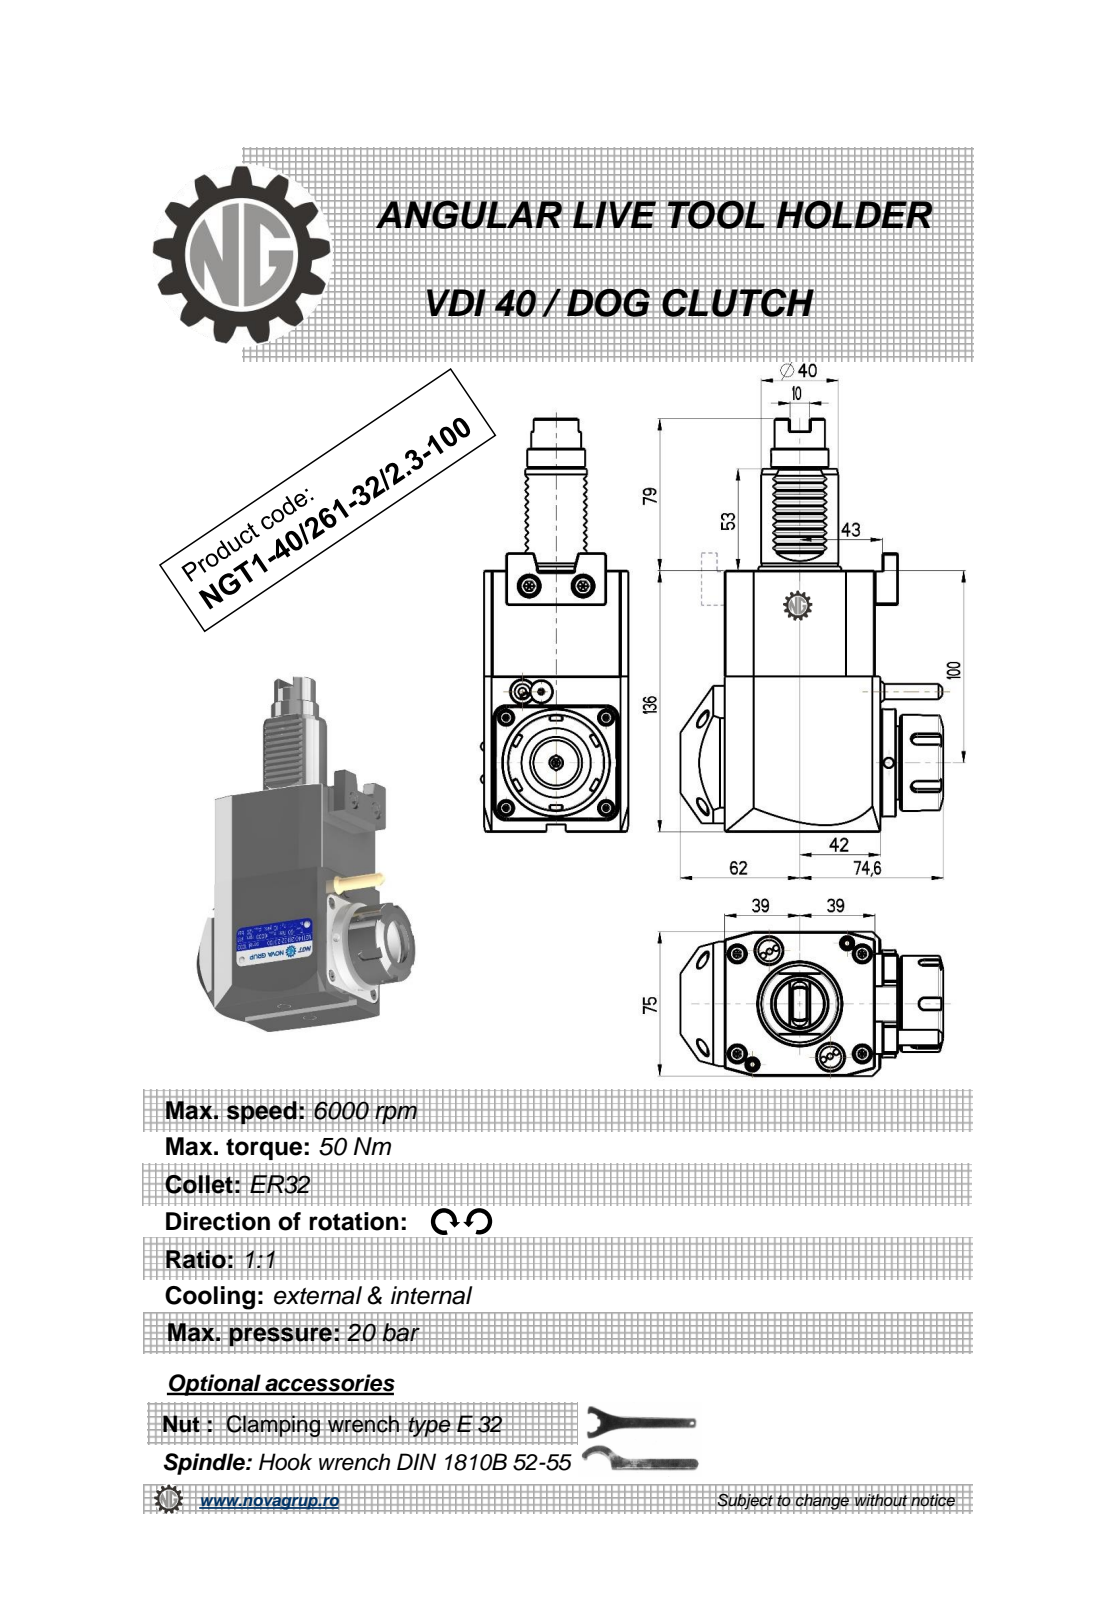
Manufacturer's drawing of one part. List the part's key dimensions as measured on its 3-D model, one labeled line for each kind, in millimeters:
Part name (STEP PRODUCT): NGT1_40_261_32_2_3_100
STEP written by: PRO/ENGINEER BY PARAMETRIC TECHNOLOGY CORPORATION, 2010280 (CONFIG_CONTROL_DESIGN)
Units: millimetres
Bodies: 1 solid, 423 faces (227 planar, 77 cylindrical, 119 other)
Overall size (bounding box): 215 × 136.6 × 75
Volume: 1 012 000 mm³ · Surface area: 78 043 mm²
Round holes (diameter × count): ⌀5 ×3, ⌀3 ×1, ⌀4.2 ×1, ⌀27 ×1
Round bosses / shafts (diameter × count): ⌀56 ×1, ⌀50 ×1, ⌀43 ×1, ⌀40 ×1, ⌀30 ×1, ⌀26 ×1, ⌀11.2 ×1, ⌀8 ×1
Partial cylindrical surfaces — rounded edges, fillets, slot ends (radius × count): R0.3 ×20, R0.22 ×6, R3 ×5, R0.5 ×2, R1 ×2, R12.5 ×1, R40 ×1
Main face-to-face distances: 75, 136, 78, 81, 0.5, 3, 84.88, 1, 80.8, 2.8
Hole centre spacings: 40.93, 122.75, 158.5
